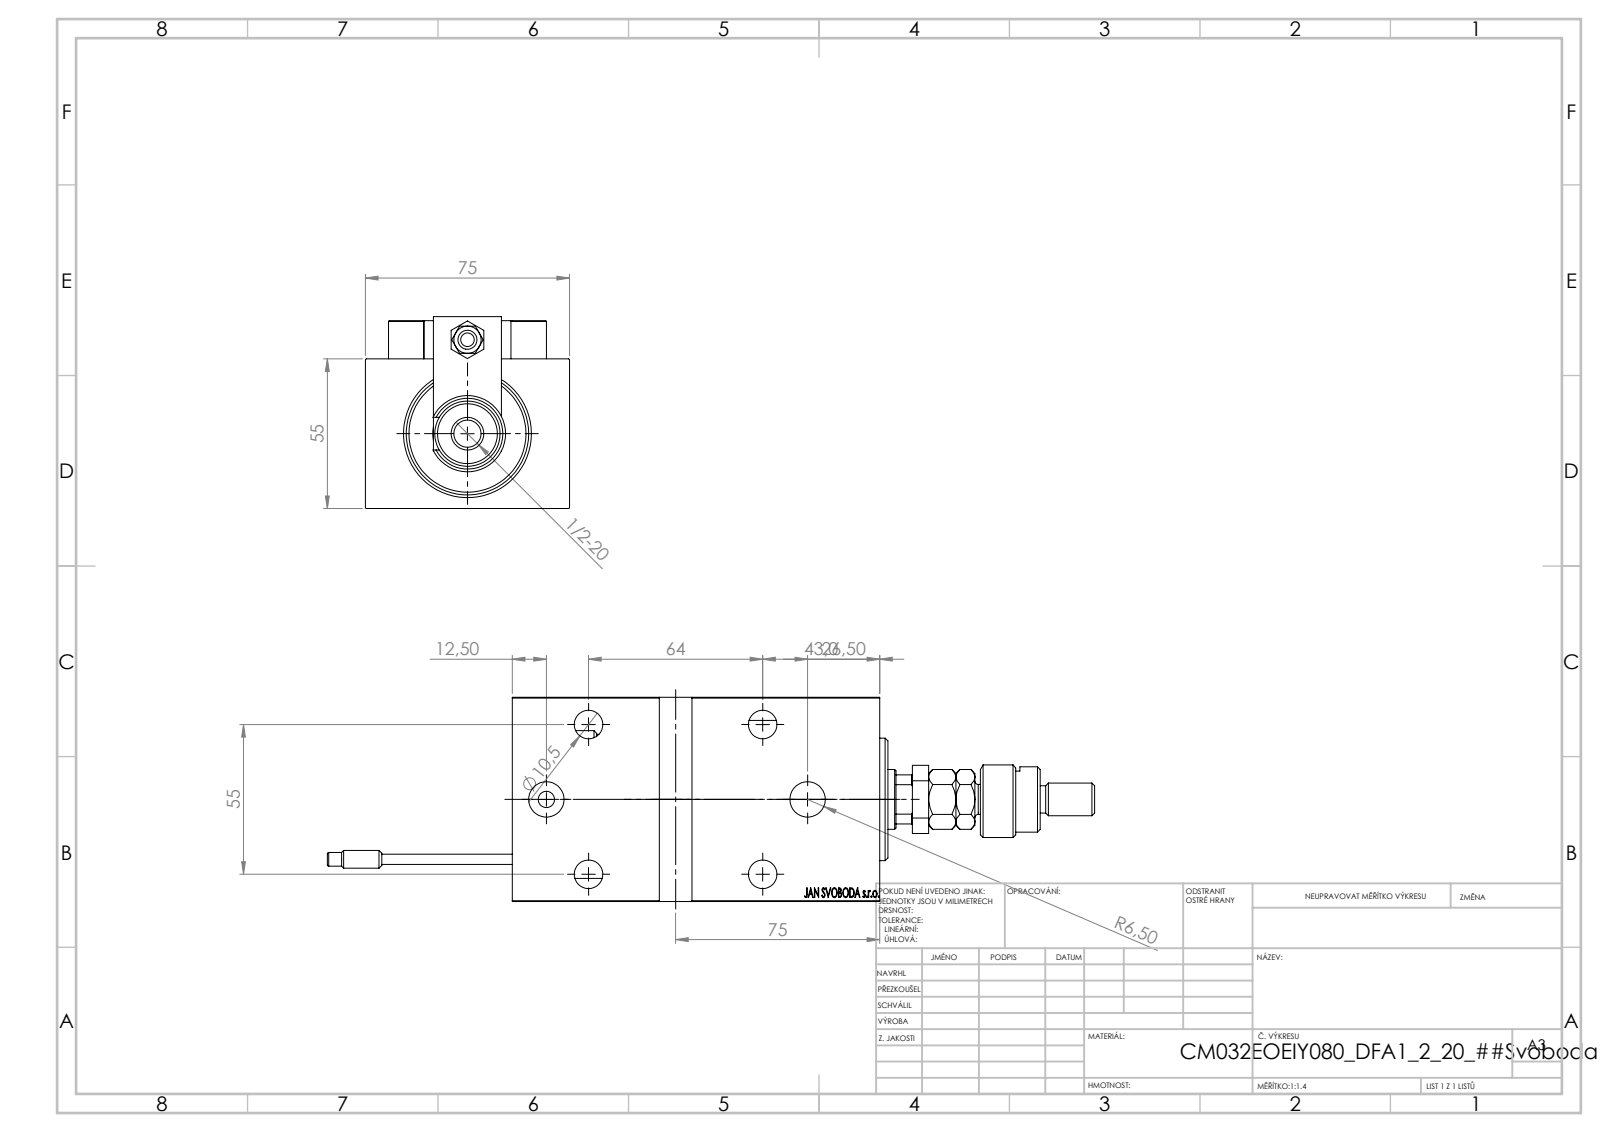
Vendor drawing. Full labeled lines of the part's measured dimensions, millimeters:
Part name (STEP PRODUCT): V450CM_VC_B; TYC_L79; SWITCH DIM B,W; KONCOVKA_Y (+7 more)
STEP written by: SolidWorks 2019 (CONFIG_CONTROL_DESIGN)
Units: millimetres
Bodies: 26 solids, 1390 faces (598 planar, 195 cylindrical, 597 other)
Overall size (bounding box): 282 × 75 × 70.5
Volume: 571 468 mm³ · Surface area: 116 879 mm²
Round holes (diameter × count): ⌀8 ×5, ⌀10.5 ×5, ⌀16.5 ×5, ⌀3.2 ×4, ⌀4 ×4, ⌀5 ×2, ⌀13 ×2, ⌀7 ×1, ⌀22 ×1, ⌀25.5 ×1, ⌀32 ×1, ⌀45 ×1
Round bosses / shafts (diameter × count): ⌀5 ×4, ⌀11 ×2, ⌀6.5 ×2, ⌀3.8 ×2, ⌀34 ×1, ⌀28 ×1, ⌀24 ×1, ⌀18 ×1
Partial cylindrical surfaces — rounded edges, fillets, slot ends (radius × count): R0.3 ×30, R3 ×2, R9.75 ×1, R10.5 ×1
Main face-to-face distances: 55, 75, 69, 14, 10, 3, 135, 25, 18, 12
Hole centre spacings: 11.37, 12.5, 20, 21.91, 28.9, 29.59, 29.69, 31.57
